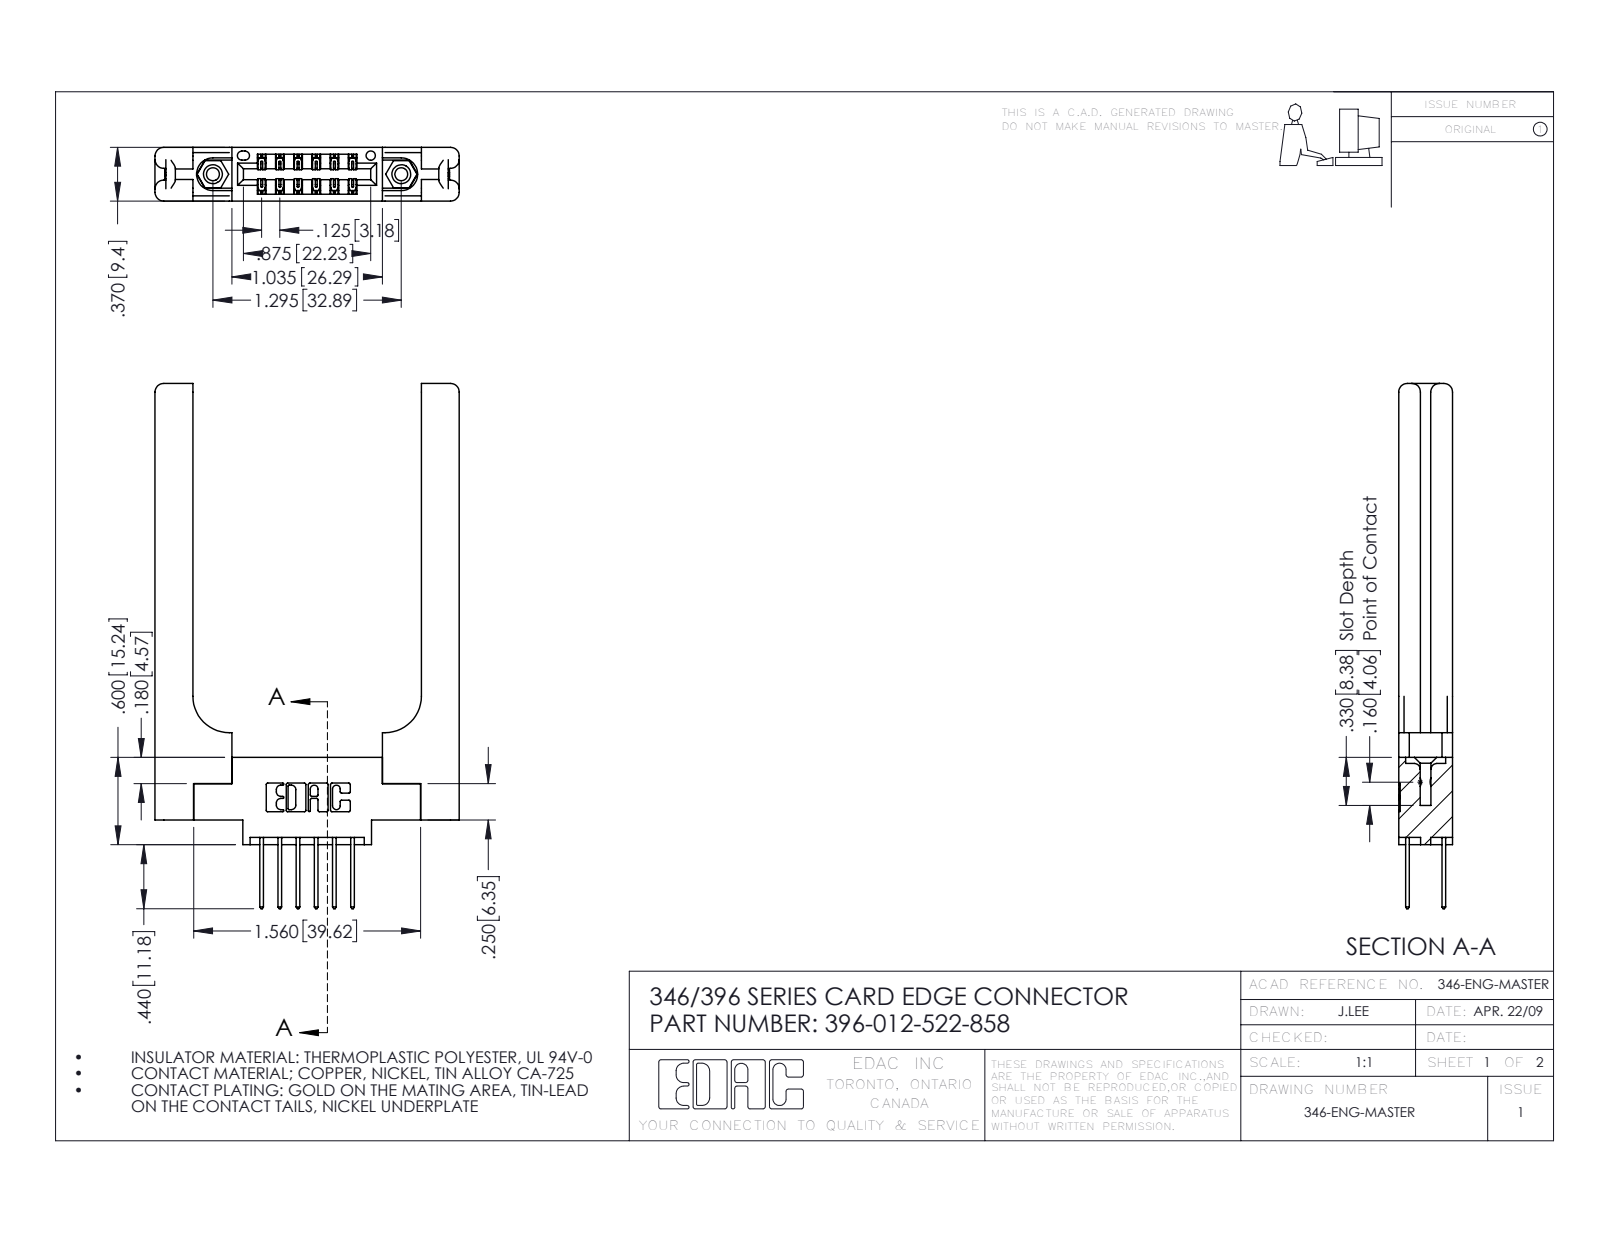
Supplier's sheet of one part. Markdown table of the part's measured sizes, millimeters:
| quantity | value |
| --- | --- |
| part name | 345-292-001_345-293-122; 396-012-522-858; 346-220-058_345-220-058; 346 Part_0.170 Offset - 0.156 Dia-TH (+1 more) |
| STEP written by | SolidWorks 2016 (CONFIG_CONTROL_DESIGN) |
| units | millimeters |
| bodies | 17 solids, 1006 faces (648 planar, 298 cylindrical, 60 other) |
| overall size | 91.7 × 53.1 × 9.4 |
| volume | 12 300 mm³ |
| surface area | 11 290 mm² |
| round holes (diameter × count) | 2.3 × 2, 3.2 × 2, 4 × 2, 1.6 × 1 |
| round bosses / shafts (diameter × count) | 3.9 × 2 |
| partial cylindrical surfaces (radius × count) | 0.3 × 22, 0.2 × 18, 1.5 × 16, 0.3 × 12, 0.2 × 6, 0.8 × 6, 0.7 × 3, 0.4 × 2 |
| main face-to-face distances | 9.4, 3.8, 5.6, 1.8, 6.4, 3.8, 2.6, 1.2, 8.2, 4.4 |
| hole center spacings | 6.2, 27.7, 32.9 |
